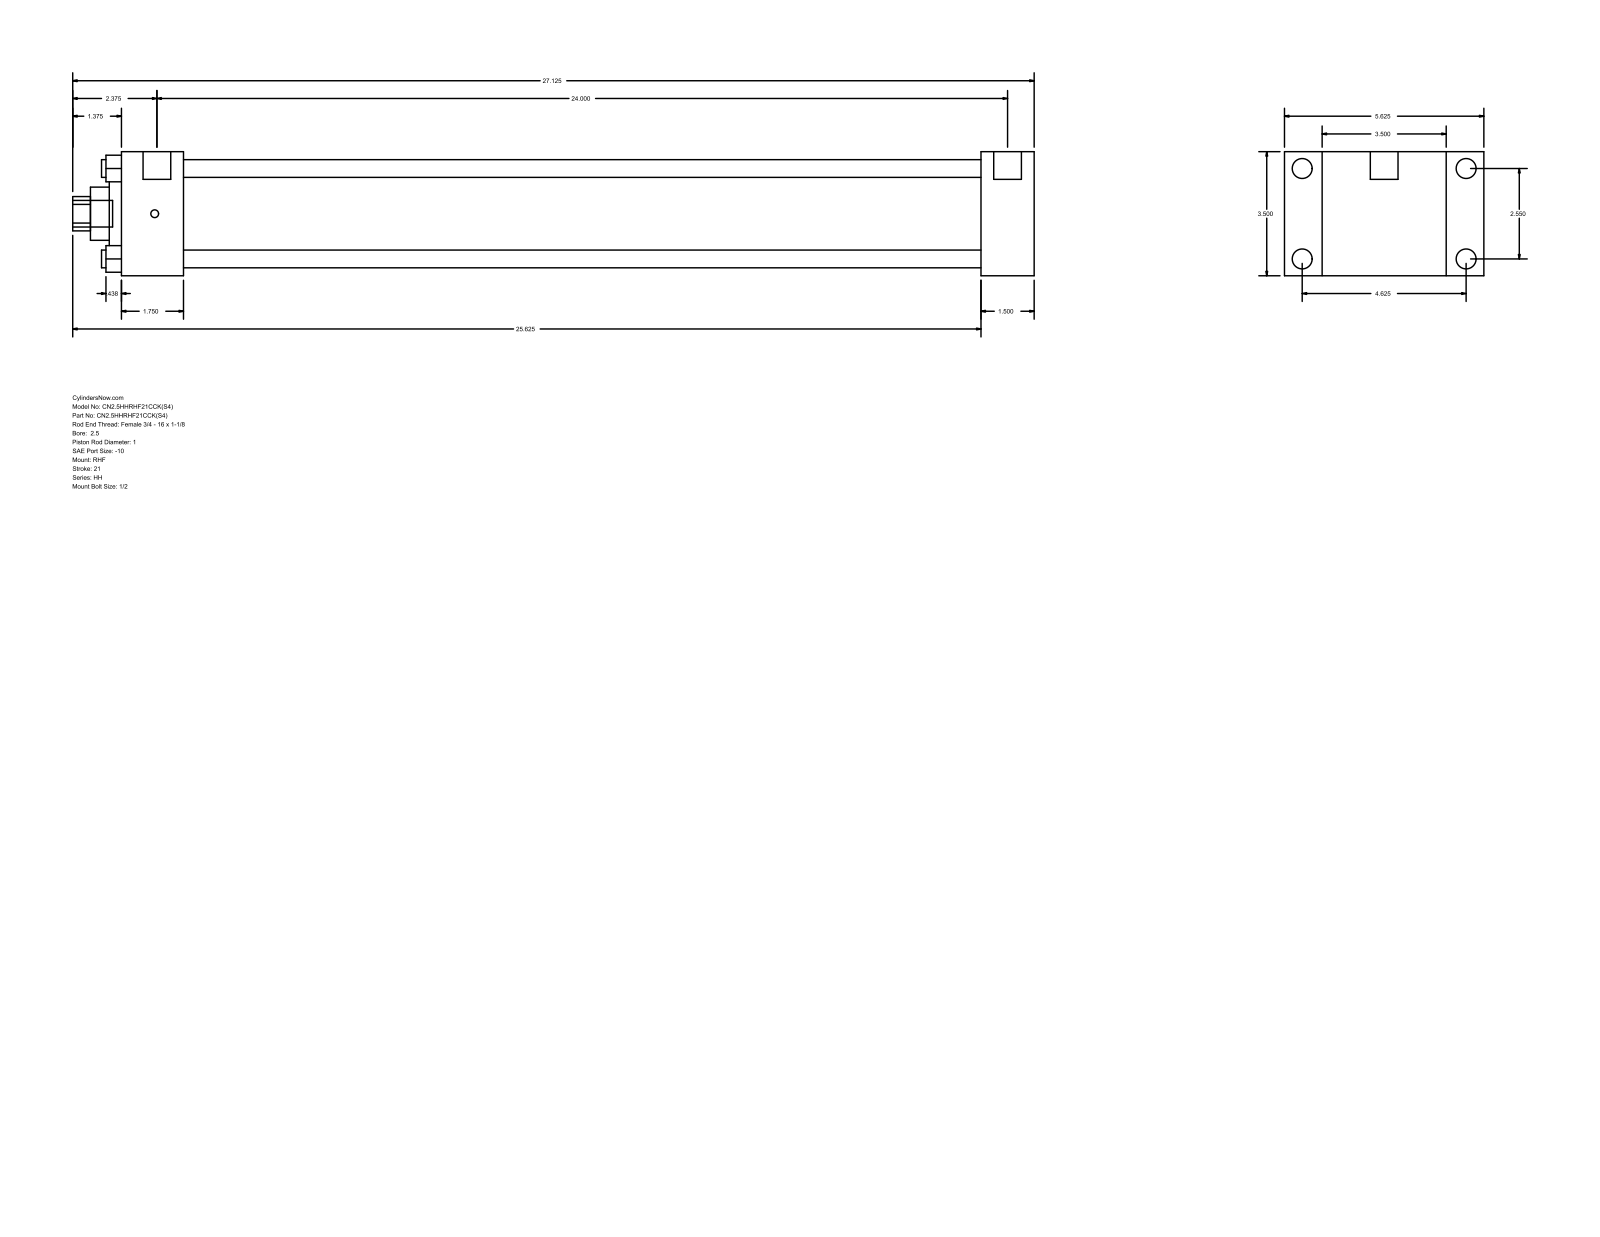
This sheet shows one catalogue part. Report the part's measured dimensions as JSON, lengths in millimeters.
{"part_name": "HH_RHF__0250_1", "step_written_by": "GSSL Pune (CONFIG_CONTROL_DESIGN)", "units": "millimeters", "bodies": {"solids": 0, "faces": 90, "planar": 61, "cylindrical": 29, "other": 0}, "overall_size": [688.98, 142.88, 88.9], "round_holes": [[12.7, 4], [25.4, 1], [38.1, 1], [60.33, 1], [73.03, 1]], "round_bosses_or_shafts": [[14.3, 4], [5.56, 4], [19.84, 2], [19.05, 1]], "partial_cylinders_radius": [[12.29, 1]], "face_to_face_distances": [88.9, 38.1, 26.99, 115.89, 615.96, 654.06, 142.88, 44.46, 571.5, 609.6], "hole_center_spacings": [45.79, 64.76, 91.58]}
